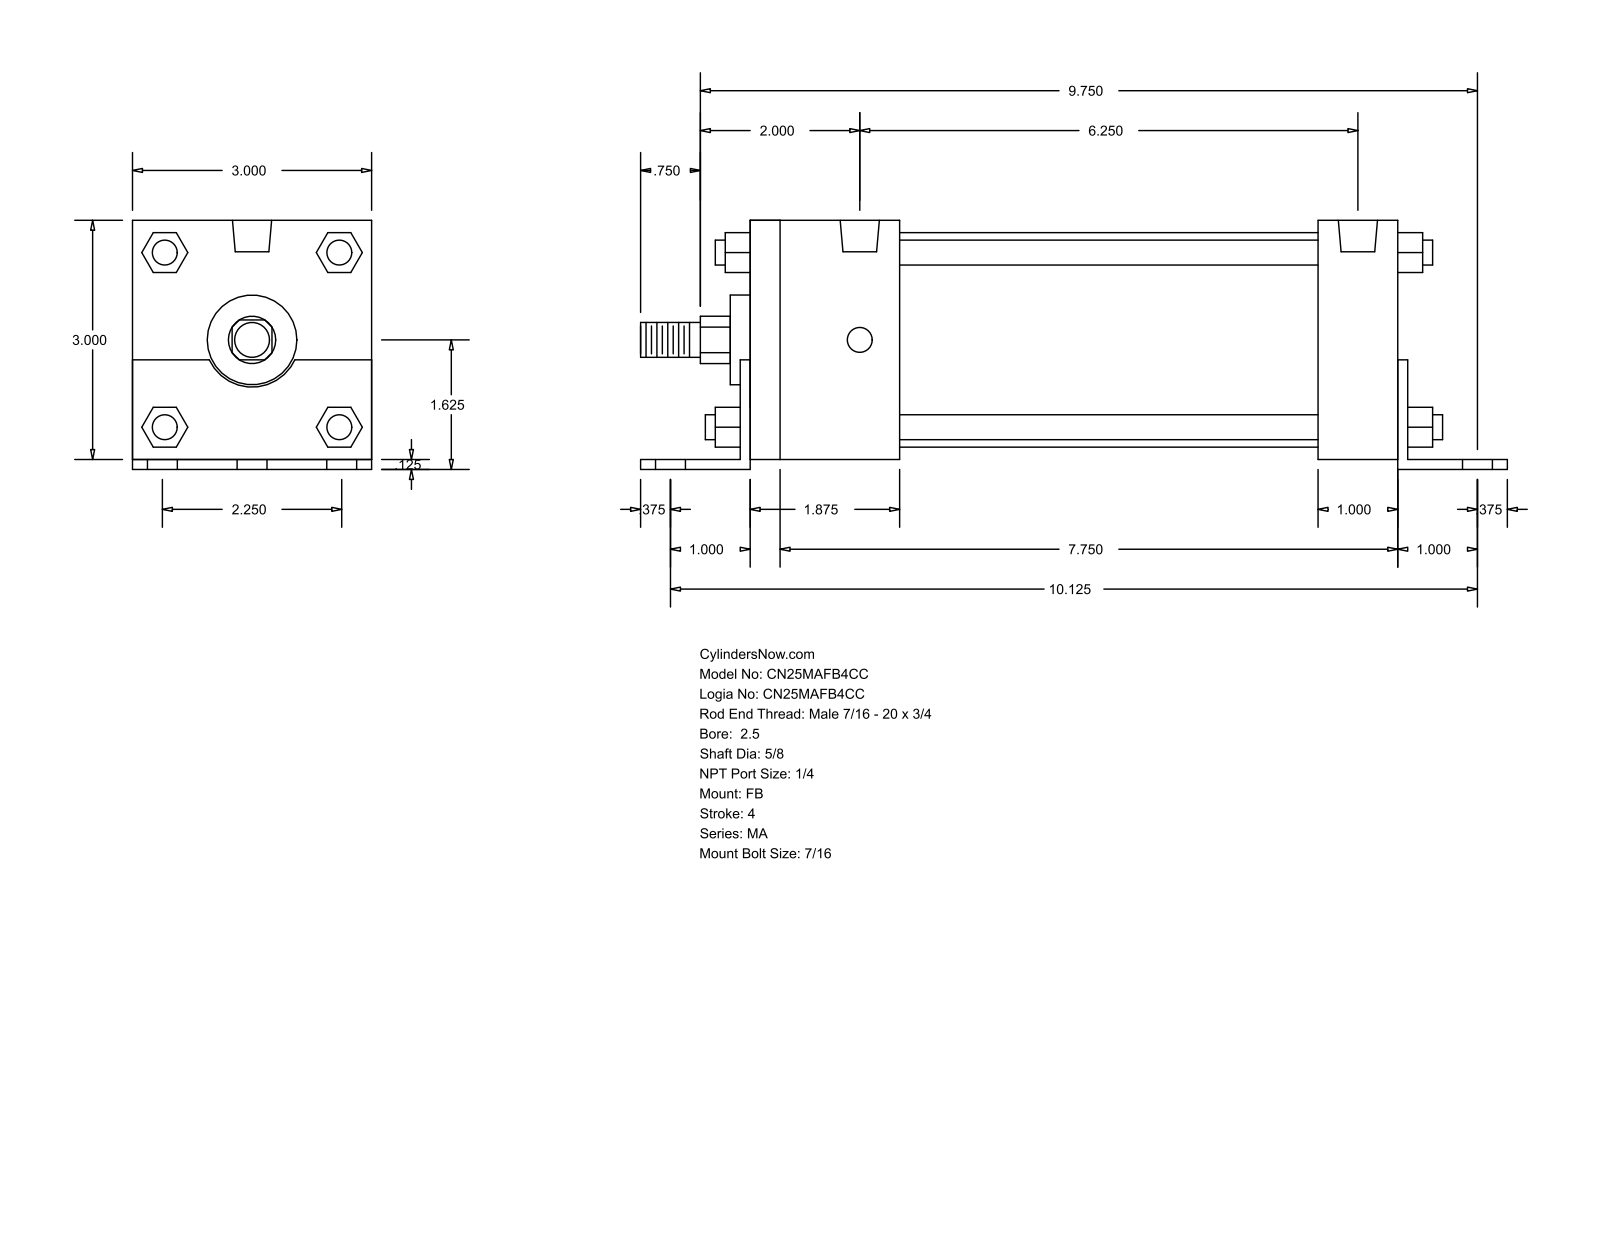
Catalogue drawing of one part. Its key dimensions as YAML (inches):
part_name: "MA_FB__0250_0.625"
step_written_by: "GSSL Pune (CONFIG_CONTROL_DESIGN)"
units: inches
bodies: {solids: 0, faces: 140, planar: 105, cylindrical: 35, other: 0}
overall_size: [10.875, 3.125, 3]
round_holes:
  - {diameter: 0.437, count: 6}
  - {diameter: 0.313, count: 4}
  - {diameter: 0.492, count: 2}
round_bosses_or_shafts:
  - {diameter: 0.313, count: 4}
  - {diameter: 2.69, count: 1}
  - {diameter: 1.125, count: 1}
  - {diameter: 0.625, count: 1}
  - {diameter: 0.437, count: 1}
partial_cylinders:
  - {radius: 0.297, count: 1}
  - {radius: 0.593, count: 1}
face_to_face_distances: [3, 0.125, 3.125, 0.125, 8.25, 8.125, 1.125, 1.875, 1, 8.375]
hole_center_spacings: [1.125, 10.187, 10.125, 1.875, 2.25, 2.628, 6.25, 7.831]
